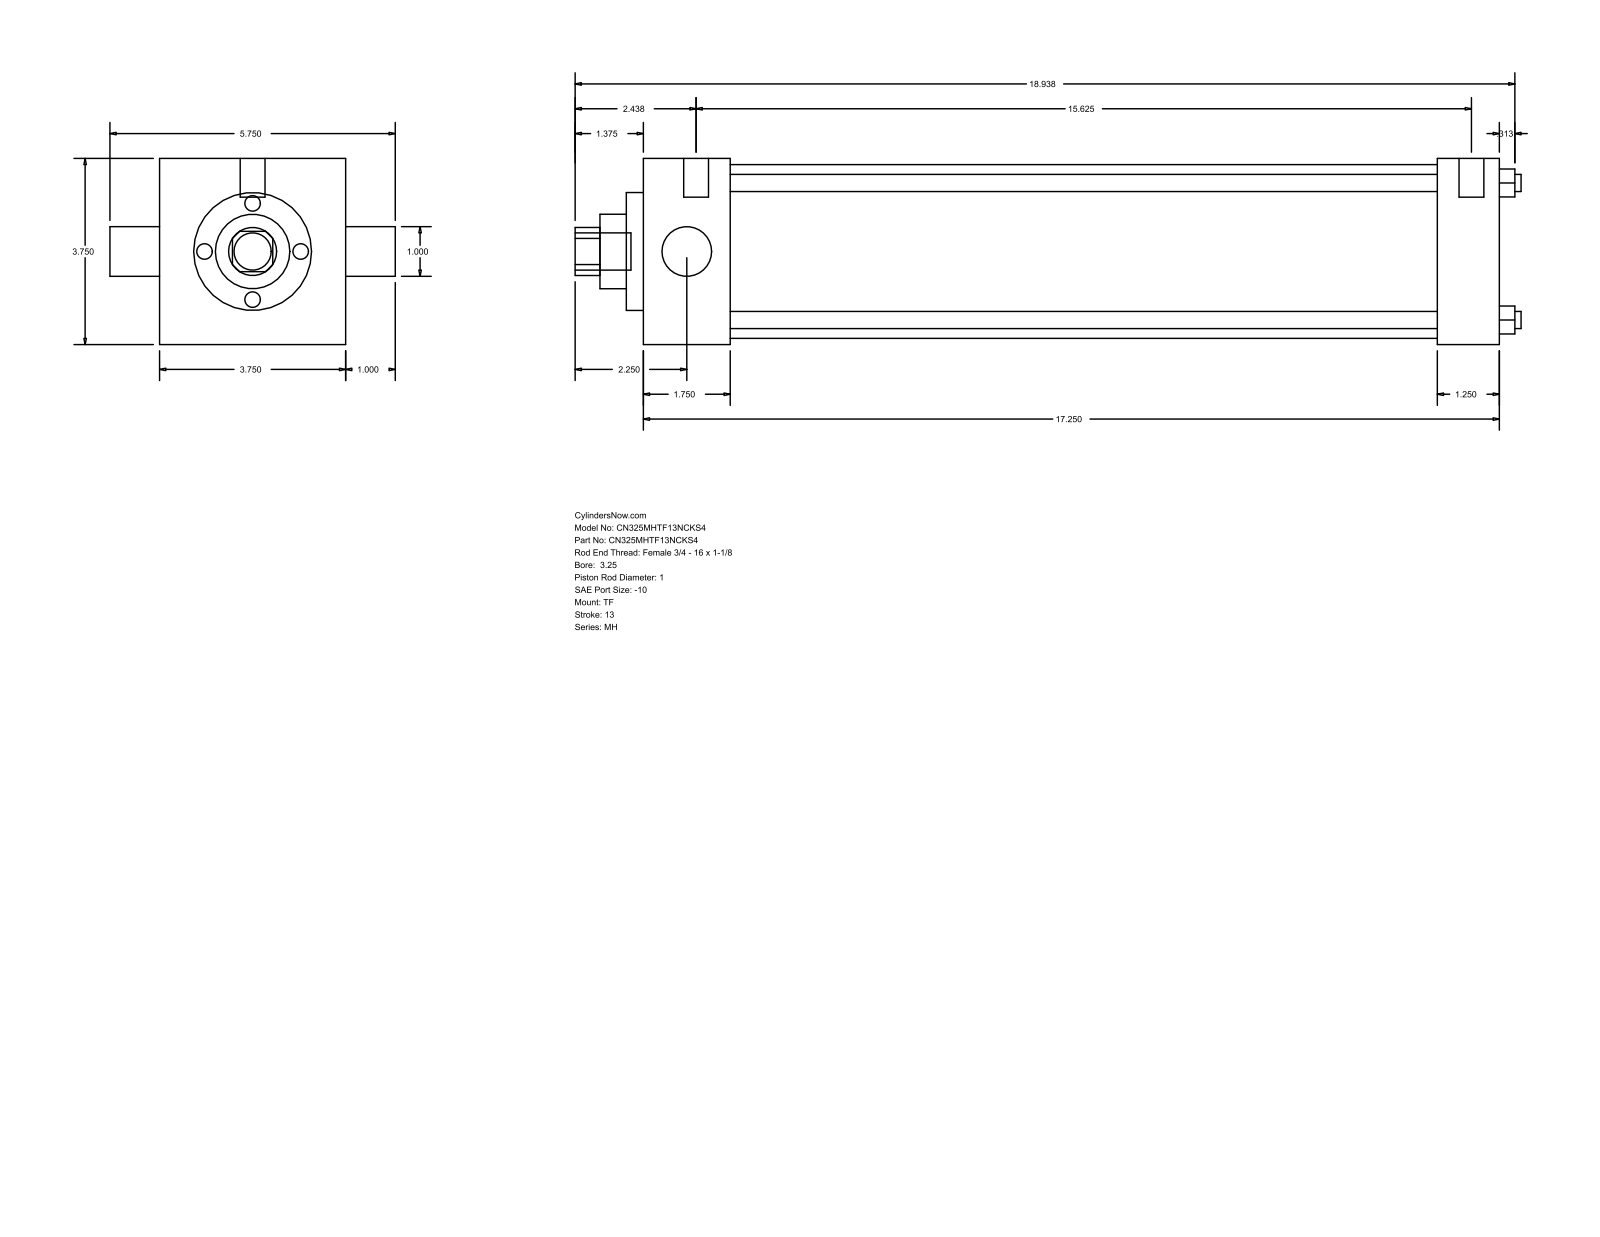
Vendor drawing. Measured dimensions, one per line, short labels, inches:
name: MH_TF__0325_1
written by: GSSL Pune (CONFIG_CONTROL_DESIGN)
unit: in
bodies: 0 solids, 86 faces (61 planar, 25 cylindrical, 0 other)
size: 19.063 × 5.75 × 3.75
holes: 4× ⌀0.345, 2× ⌀1, 1× ⌀1.5, 1× ⌀2.375, 1× ⌀3.5
bosses: 3× ⌀0.219, 2× ⌀0.5, 1× ⌀0.75
rounds: 1× R0.484
face distances: 3.75, 17.25, 1.75, 16, 14.25, 15.5, 1.25, 0.344, 2.094, 16.344
hole spacings: 1.952, 2.76, 3.903
